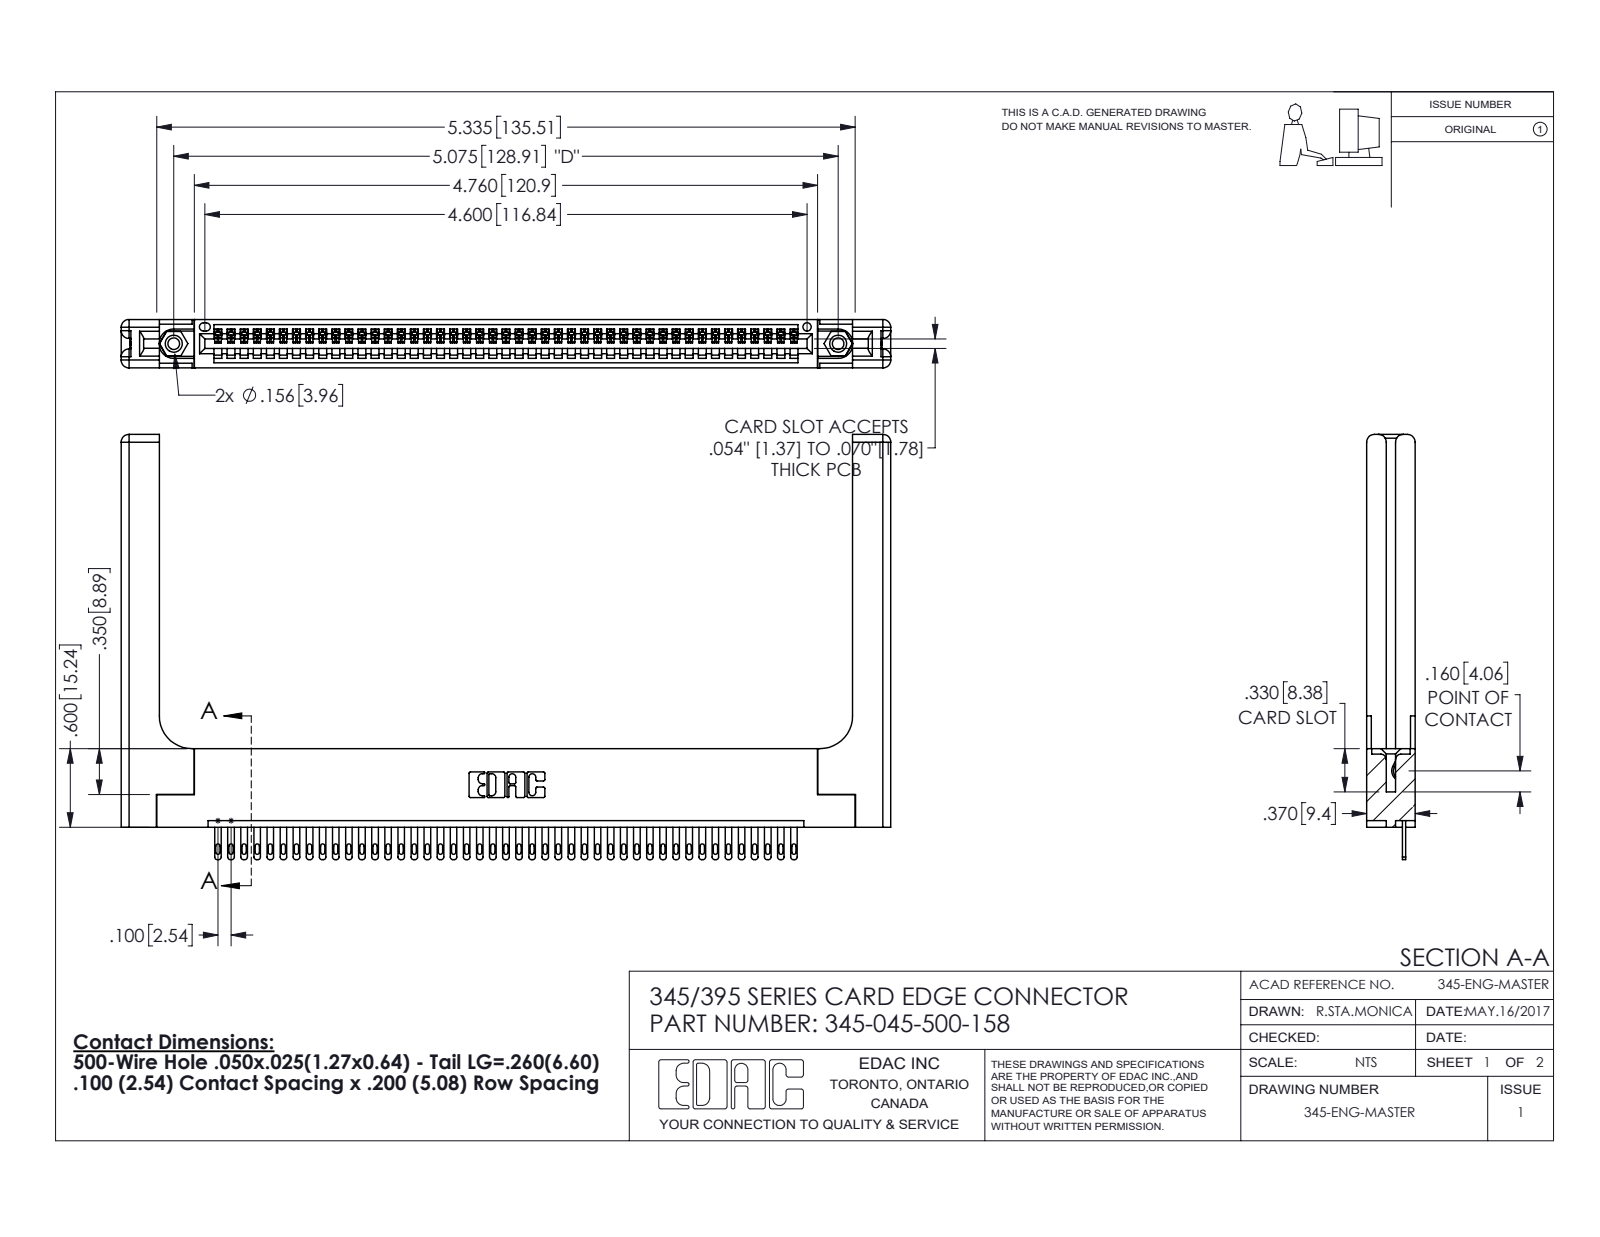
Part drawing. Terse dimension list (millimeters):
name: 345 Part_Flush Mounting Lugs - 0.156 Dia-TH; 345-045-500-158; 345-250-001_345-250-001-102; 345-220-058_345-220-058 (+1 more)
written by: SolidWorks 2016 (CONFIG_CONTROL_DESIGN)
unit: mm
bodies: 50 solids, 2812 faces (1758 planar, 994 cylindrical, 60 other)
size: 149.3 × 82.5 × 9.4
volume: 22 750 mm³; area: 24 370 mm²
holes: 2× ⌀2.3, 2× ⌀3.2, 2× ⌀4, 1× ⌀1.6
bosses: 2× ⌀3.9
rounds: 90× R0.2, 90× R0.4, 90× R0.5, 22× R0.3, 16× R1.5, 6× R0.2, 6× R0.8, 3× R0.7
face distances: 1.8, 9.4, 7.6, 5.1, 2.5, 6.9, 0.6, 5.7, 3.8, 3.8
hole spacings: 6.9, 122.9, 128.9
